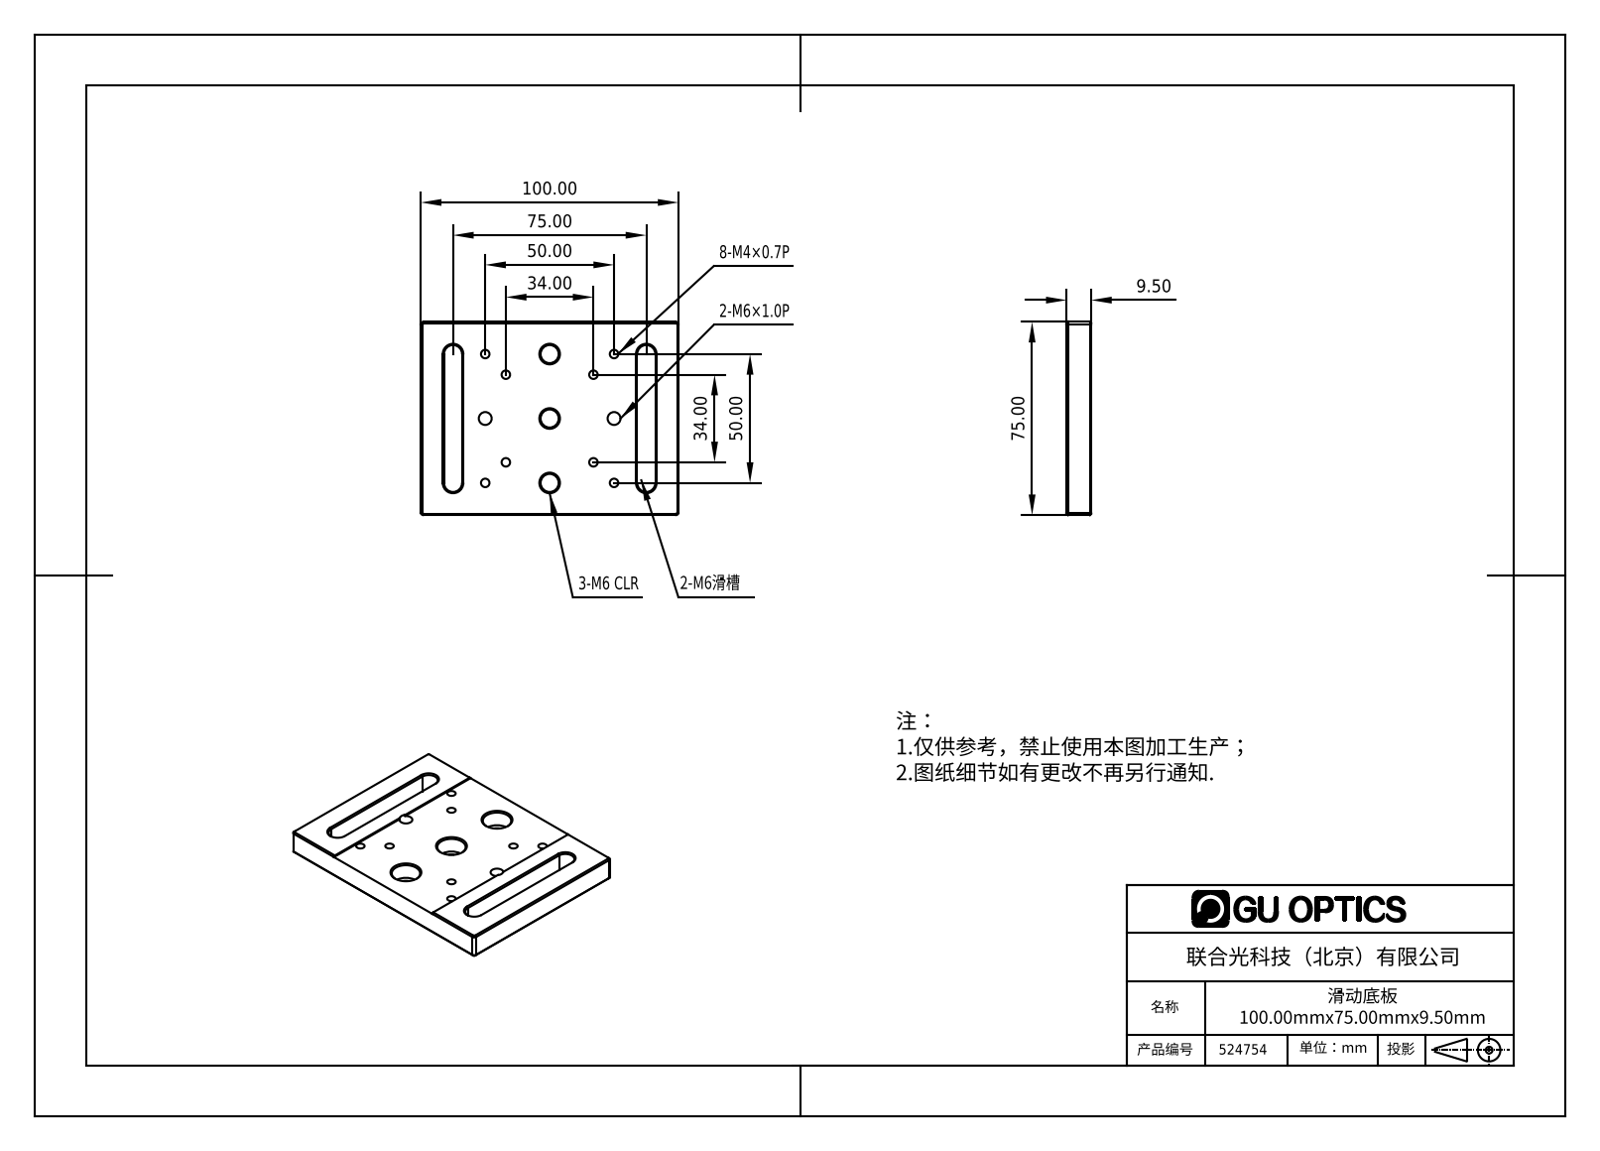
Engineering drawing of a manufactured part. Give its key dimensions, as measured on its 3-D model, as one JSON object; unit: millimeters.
{"part_name": "SB-3", "step_written_by": "SolidWorks 2012 (CONFIG_CONTROL_DESIGN)", "units": "millimeters", "bodies": {"solids": 1, "faces": 83, "planar": 37, "cylindrical": 24, "other": 22}, "overall_size": [100, 75, 9.5], "volume_mm3": 58567, "surface_area_mm2": 20151, "round_holes": [[3.3, 8], [7, 3], [11, 3], [5, 2]], "partial_cylinders_radius": [[1, 4], [3.5, 4]], "face_to_face_distances": [9, 9.5, 0.5, 75, 7, 16, 84, 91, 100, 68], "hole_center_spacings": [18.79, 25, 45.31, 35.36, 50, 24.04, 34, 42.75]}
